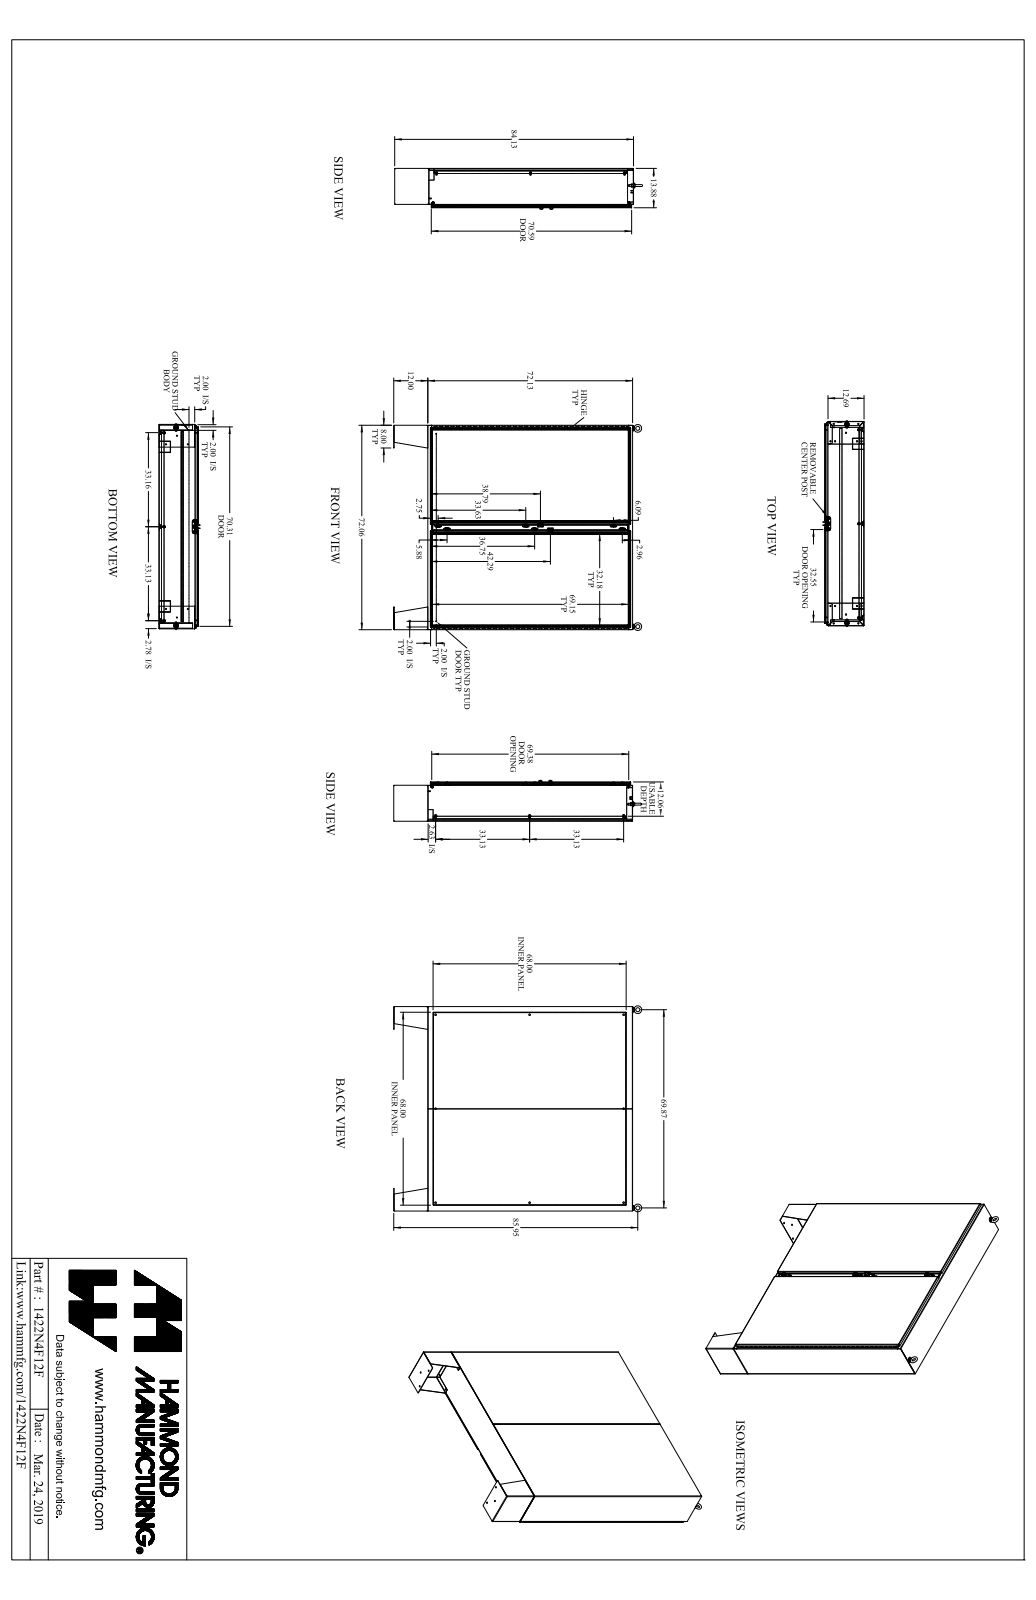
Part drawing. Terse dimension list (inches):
name: 1422N4F12F_Default
written by: SolidWorks 2019 (CONFIG_CONTROL_DESIGN)
unit: in
bodies: 109 solids, 3636 faces (1846 planar, 1578 cylindrical, 212 other)
size: 87.778 × 73.129 × 14.468
volume: 2 435 in³; area: 45 676 in²
holes: 24× ⌀0.304, 14× ⌀0.437, 8× ⌀0.307, 8× ⌀0.563, 6× ⌀0.213, 6× ⌀0.265, 6× ⌀0.375, 6× ⌀0.445, 3× ⌀0.201, 3× ⌀0.25, 3× ⌀0.313, 2× ⌀0.11
bosses: 8× ⌀1, 8× ⌀0.65, 8× ⌀0.375, 8× ⌀0.33, 6× ⌀0.5, 6× ⌀0.39, 6× ⌀0.244, 4× ⌀0.281
rounds: 67× R0.048, 67× R0.143, 34× R0.25, 18× R0.06, 14× R0.187, 12× R0.116, 12× R0.141, 12× R0.185
face distances: 0.095, 0.125, 13.78, 13.655, 13.75, 13.875, 0.125, 11.968, 12.063, 1.687
hole spacings: 6, 70.461, 12, 71.223, 18, 72.476, 24, 74.194
